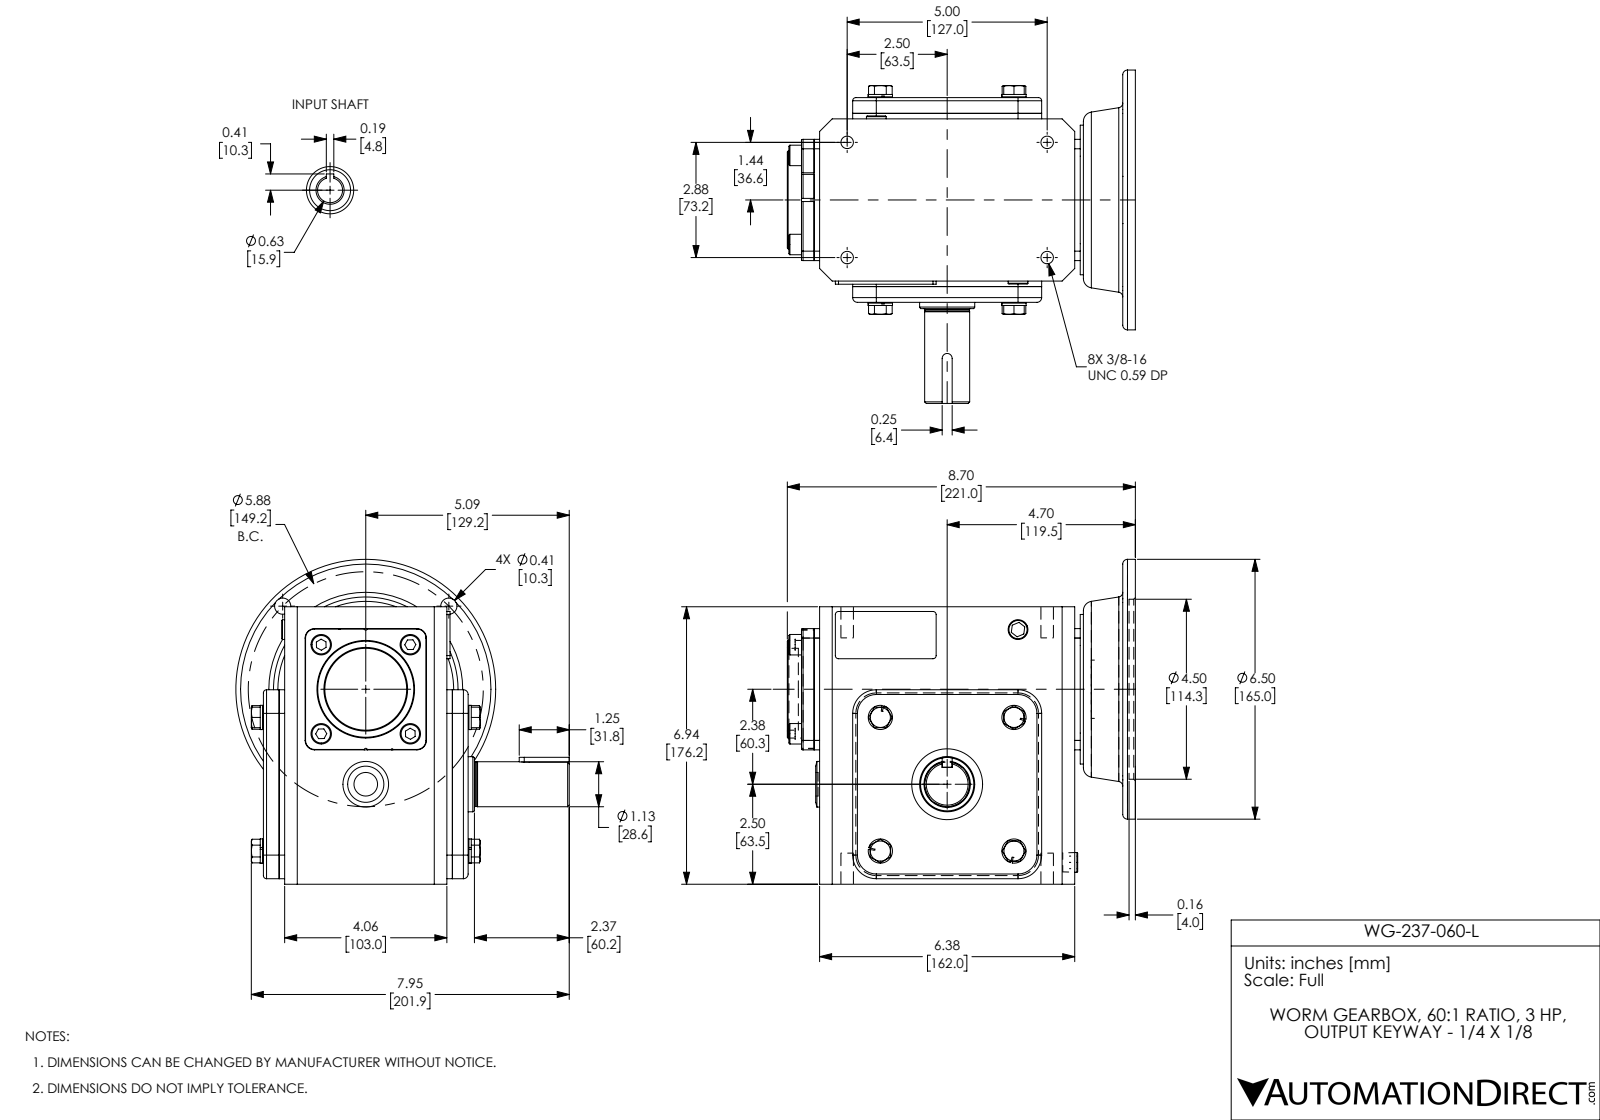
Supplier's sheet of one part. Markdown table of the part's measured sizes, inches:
| quantity | value |
| --- | --- |
| part name | WG-237-060-L |
| STEP written by | SolidWorks 2017 (AUTOMOTIVE_DESIGN) |
| units | inches |
| bodies | 37 solids, 542 faces (295 planar, 157 cylindrical, 90 other) |
| overall size | 8.701 × 8.335 × 8.123 |
| volume | 220.2 in³ |
| surface area | 513.5 in² |
| round holes (diameter × count) | 0.313 × 4, 0.406 × 4, 0.591 × 1, 0.625 × 1, 1.181 × 1, 1.378 × 1, 1.457 × 1, 1.772 × 1, 3.819 × 1, 4.5 × 1 |
| round bosses / shafts (diameter × count) | 0.606 × 4, 0.512 × 4, 6.496 × 1, 3.74 × 1, 2.441 × 1, 2.047 × 1, 1.142 × 1, 1.125 × 1 |
| partial cylindrical surfaces (radius × count) | 0.079 × 12, 0.236 × 6, 0.118 × 4, 0.591 × 4, 0.02 × 2, 0.039 × 2, 0.125 × 1 |
| main face-to-face distances | 0.138, 4.724, 0.394, 4.331, 0.531, 4.193, 4.587, 6.516, 6.937, 0.315 |
| hole center spacings | 2.937, 2.098, 2.88, 4.154, 4.154, 4.913, 5, 5.77 |
